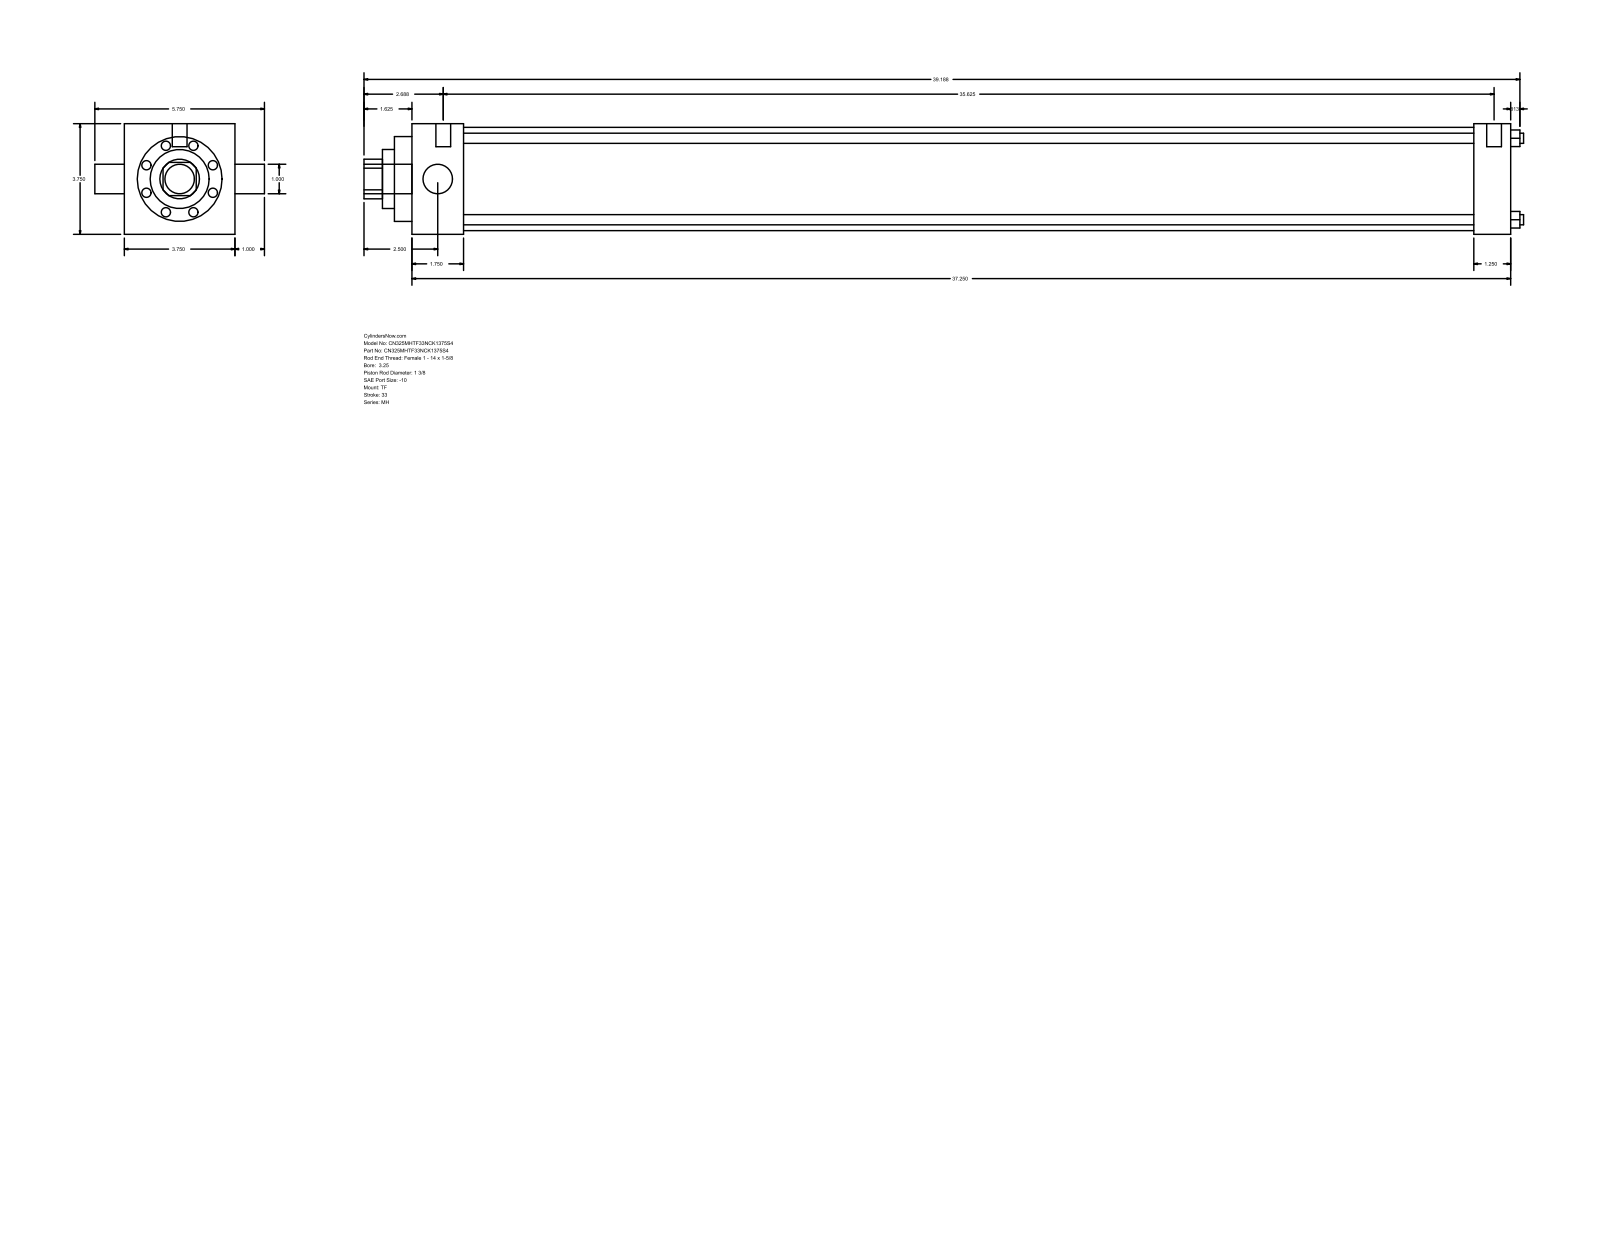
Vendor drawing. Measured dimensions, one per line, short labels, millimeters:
name: MH_TF__0325_1.375
written by: GSSL Pune (CONFIG_CONTROL_DESIGN)
unit: mm
bodies: 0 solids, 86 faces (61 planar, 25 cylindrical, 0 other)
size: 998.54 × 146.05 × 95.25
holes: 4× ⌀8.76, 1× ⌀25.4, 1× ⌀34.92, 1× ⌀50.8, 1× ⌀73.03, 1× ⌀88.9
bosses: 3× ⌀5.56, 2× ⌀12.7, 1× ⌀25.4
rounds: 1× R17.06
face distances: 95.24, 946.15, 44.45, 914.4, 869.95, 901.7, 31.75, 15.08, 59.53, 929.48
hole spacings: 49.57, 70.1, 99.14
